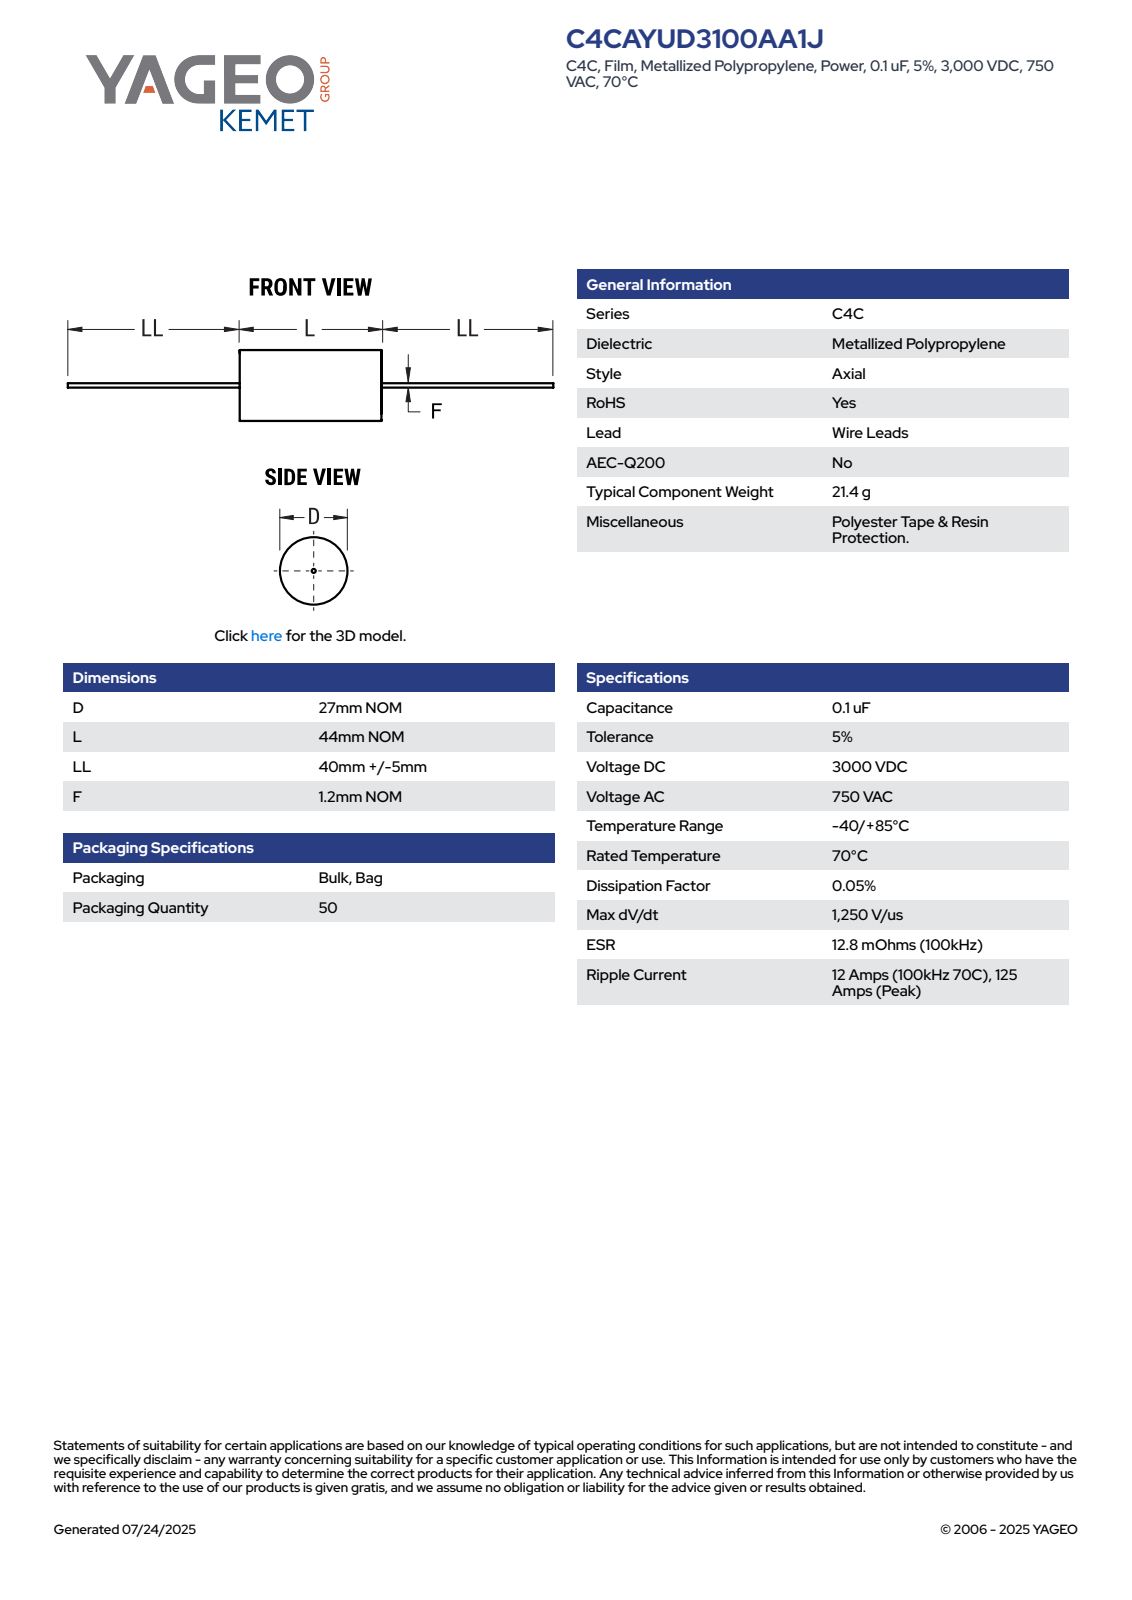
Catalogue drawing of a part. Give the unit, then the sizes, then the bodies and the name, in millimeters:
Units: millimetres
Overall size (bounding box): 134 × 27 × 27
Round bosses / shafts (diameter × count): ⌀27 ×1, ⌀1.2 ×1
Partial cylindrical surfaces — rounded edges, fillets, slot ends (radius × count): R13.49 ×1
Main face-to-face distances: 44, 43.99, 44.99, 45, 88.99, 134, 89.01, 89, 45.01
Volume: 25 294 mm³ · Surface area: 6 360 mm²
Bodies: 2 solids, 87 faces (28 planar, 28 cylindrical, 31 other)
Part name (STEP PRODUCT): CFP_ACWF_27X44_D27L44LL45F1.2
STEP written by: SolidWorks 2014 (AUTOMOTIVE_DESIGN)
